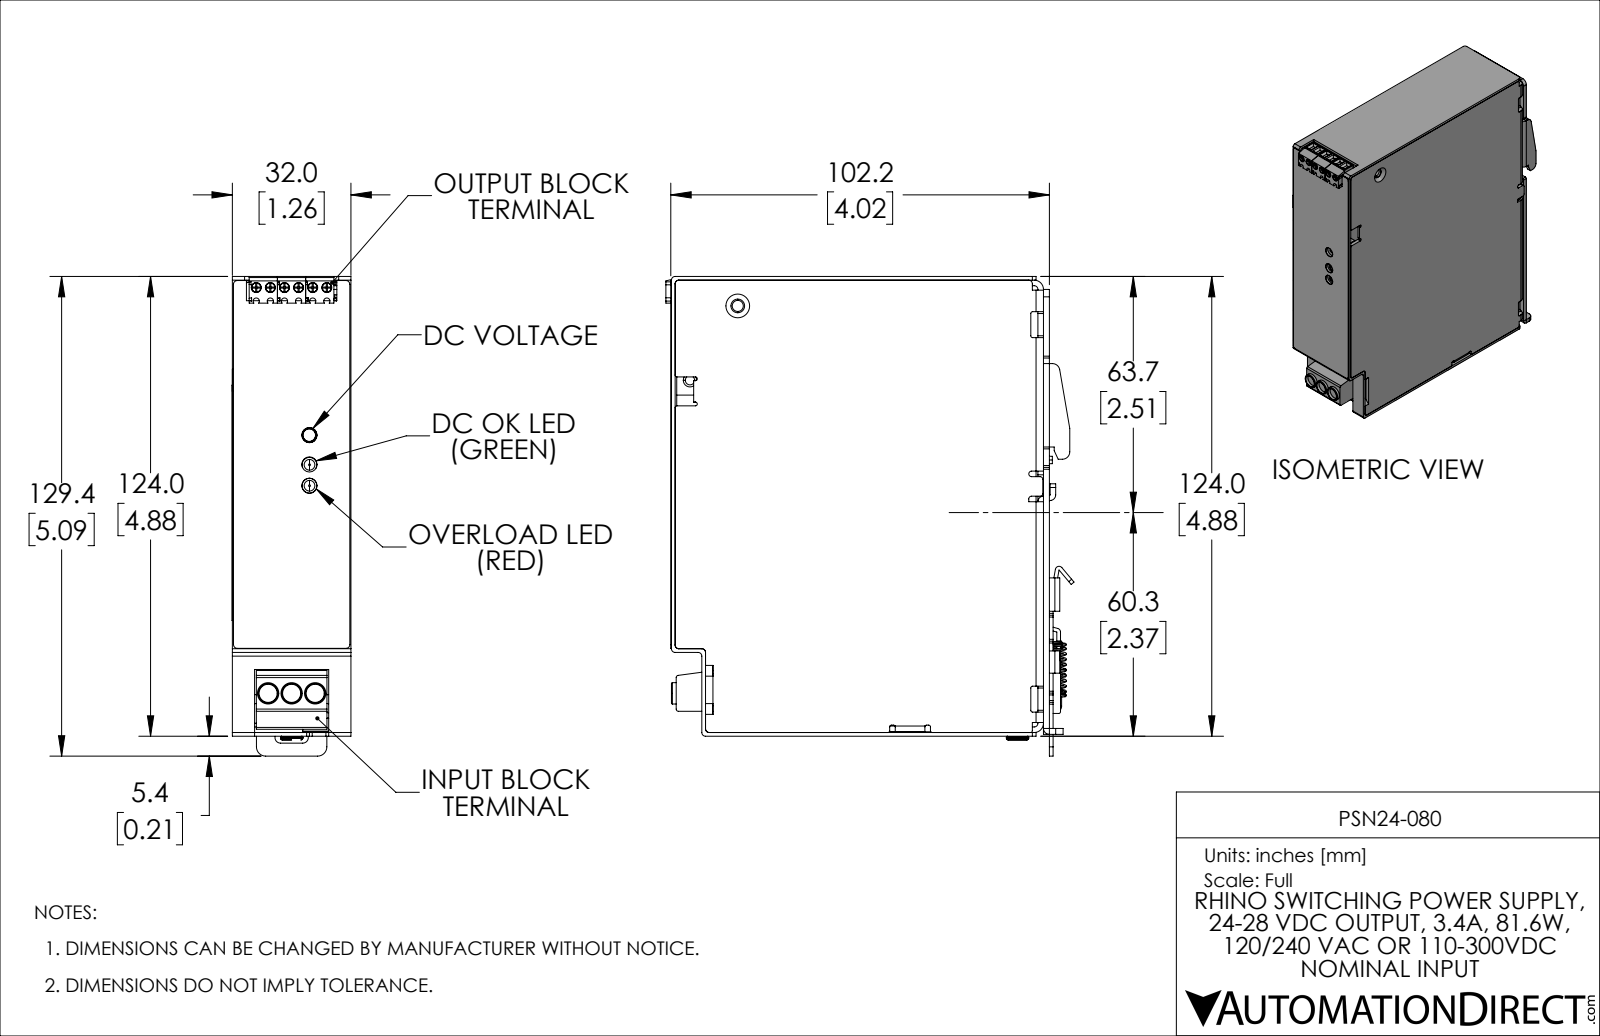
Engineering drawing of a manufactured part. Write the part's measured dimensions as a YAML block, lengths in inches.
part_name: "PSN24-080"
step_written_by: "SolidWorks 2019 (AUTOMOTIVE_DESIGN)"
units: inches
bodies: {solids: 37, faces: 1853, planar: 1225, cylindrical: 478, other: 150}
overall_size: [5.093, 4.336, 1.263]
volume: 4.519
surface_area: 216
round_holes:
  - {diameter: 0.098, count: 6}
  - {diameter: 0.1, count: 6}
  - {diameter: 0.177, count: 4}
  - {diameter: 0.157, count: 3}
  - {diameter: 0.193, count: 3}
  - {diameter: 0.083, count: 2}
  - {diameter: 0.142, count: 2}
  - {diameter: 0.079, count: 1}
  - {diameter: 0.118, count: 1}
  - {diameter: 0.13, count: 1}
  - {diameter: 0.138, count: 1}
  - {diameter: 0.146, count: 1}
round_bosses_or_shafts:
  - {diameter: 0.02, count: 24}
  - {diameter: 0.096, count: 6}
  - {diameter: 0.227, count: 3}
  - {diameter: 0.093, count: 3}
  - {diameter: 0.09, count: 3}
  - {diameter: 0.236, count: 2}
  - {diameter: 0.114, count: 2}
  - {diameter: 0.098, count: 2}
partial_cylinders:
  - {radius: 0.02, count: 99}
  - {radius: 0.039, count: 39}
  - {radius: 0.004, count: 16}
  - {radius: 0.012, count: 16}
  - {radius: 0.03, count: 16}
  - {radius: 0.079, count: 14}
  - {radius: 0.016, count: 13}
  - {radius: 0.063, count: 9}
face_to_face_distances: [0.059, 1.201, 0.017, 0.039, 1.26, 1.142, 1.184, 1.125, 0.076, 0.063]
hole_center_spacings: [0.3, 0.15, 0.15, 0.156, 0.25, 0.315, 0.394, 0.398]
